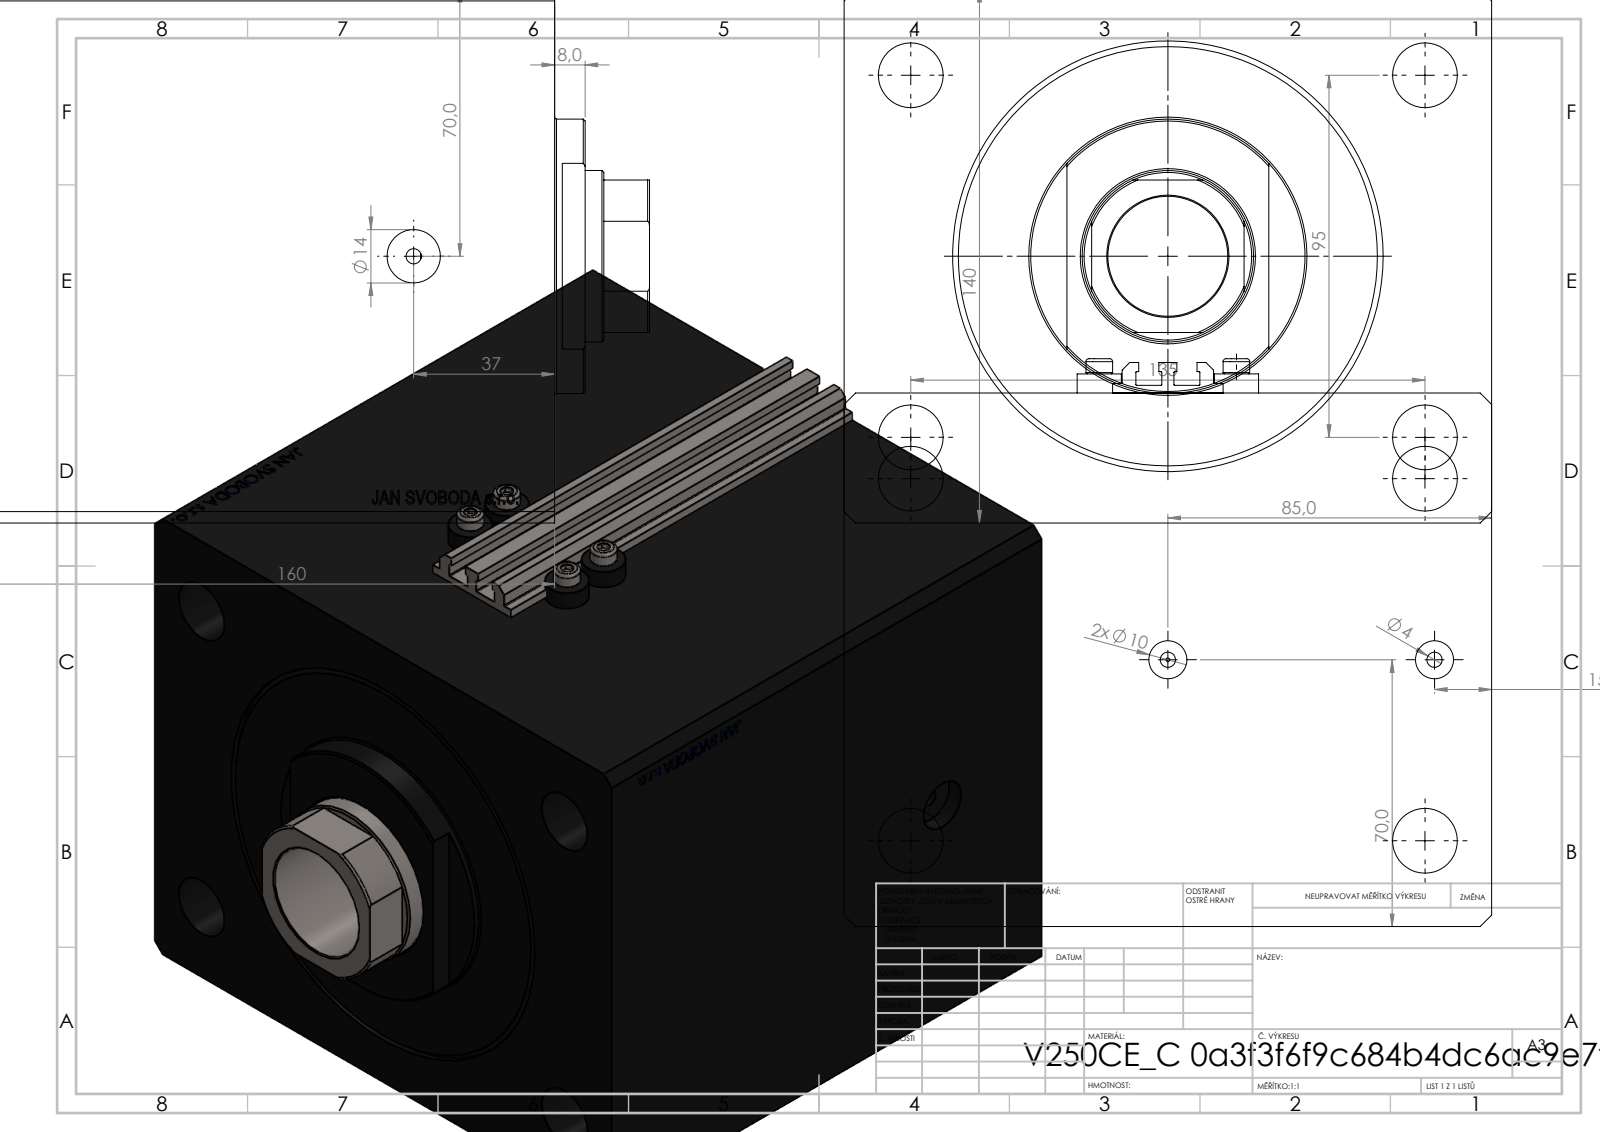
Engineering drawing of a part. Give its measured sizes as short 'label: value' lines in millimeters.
name: ALLEN BOLT V250CE; V250CE_C_VCP; V250CE_C_Body; V250CE_VC_C
written by: SolidWorks 2019 (CONFIG_CONTROL_DESIGN)
unit: mm
bodies: 8 solids, 1038 faces (504 planar, 88 cylindrical, 446 other)
size: 184.9 × 170 × 149
volume: 3 370 000 mm³; area: 326 786 mm²
holes: 8× ⌀4, 4× ⌀17, 2× ⌀10, 2× ⌀14, 1× ⌀1.25, 1× ⌀31.5, 1× ⌀45, 1× ⌀100, 1× ⌀113
bosses: 4× ⌀11.6, 4× ⌀7, 1× ⌀72
rounds: 10× R0.2, 1× R22
face distances: 140, 170, 160, 28.9, 131.1, 124.9, 96, 35.1, 50, 74.9
hole spacings: 82.54, 13.6, 36, 38.48, 47.57, 95, 135, 145.47
